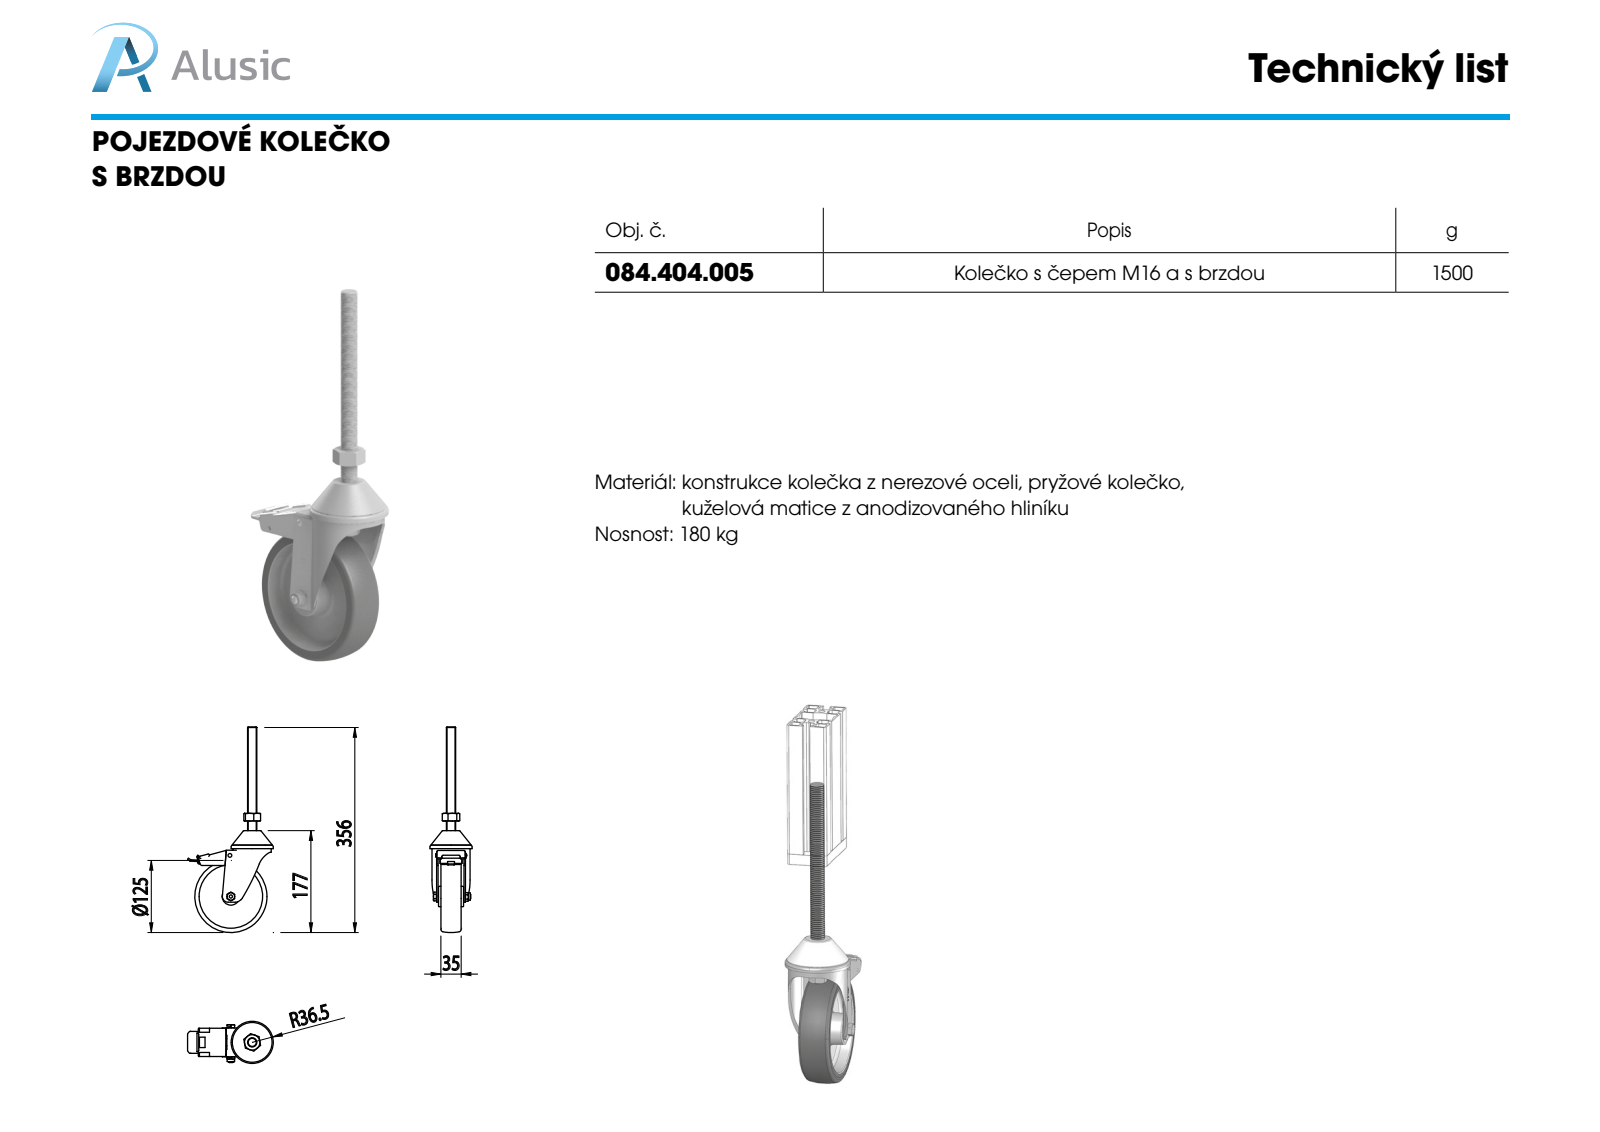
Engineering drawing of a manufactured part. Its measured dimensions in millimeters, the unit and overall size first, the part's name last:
Units: millimetres
Overall size (bounding box): 356.37 × 148.56 × 73
Round holes (diameter × count): ⌀10 ×2, ⌀2.7 ×1, ⌀8 ×1, ⌀10.8 ×1, ⌀12 ×1, ⌀61 ×1, ⌀68 ×1
Round bosses / shafts (diameter × count): ⌀16 ×2, ⌀8 ×2, ⌀110 ×1, ⌀73 ×1, ⌀66 ×1, ⌀54 ×1, ⌀30 ×1, ⌀12.81 ×1
Partial cylindrical surfaces — rounded edges, fillets, slot ends (radius × count): R2 ×14, R1 ×3, R1.5 ×3, R2.5 ×3, R4 ×3, R10 ×3, R0.5 ×2, R1.2 ×2
Main face-to-face distances: 2.5, 5, 40, 42.5, 7.5, 47.5, 2, 45, 0.5, 47
Hole centre spacings: 0.71, 10.7, 10.96, 26.42, 26.52, 35, 36.29, 45.03
Bodies: 0 solids, 460 faces (217 planar, 127 cylindrical, 116 other)
Part name (STEP PRODUCT): 084.404.005
STEP written by: SolidWorks 2011 (CONFIG_CONTROL_DESIGN)
